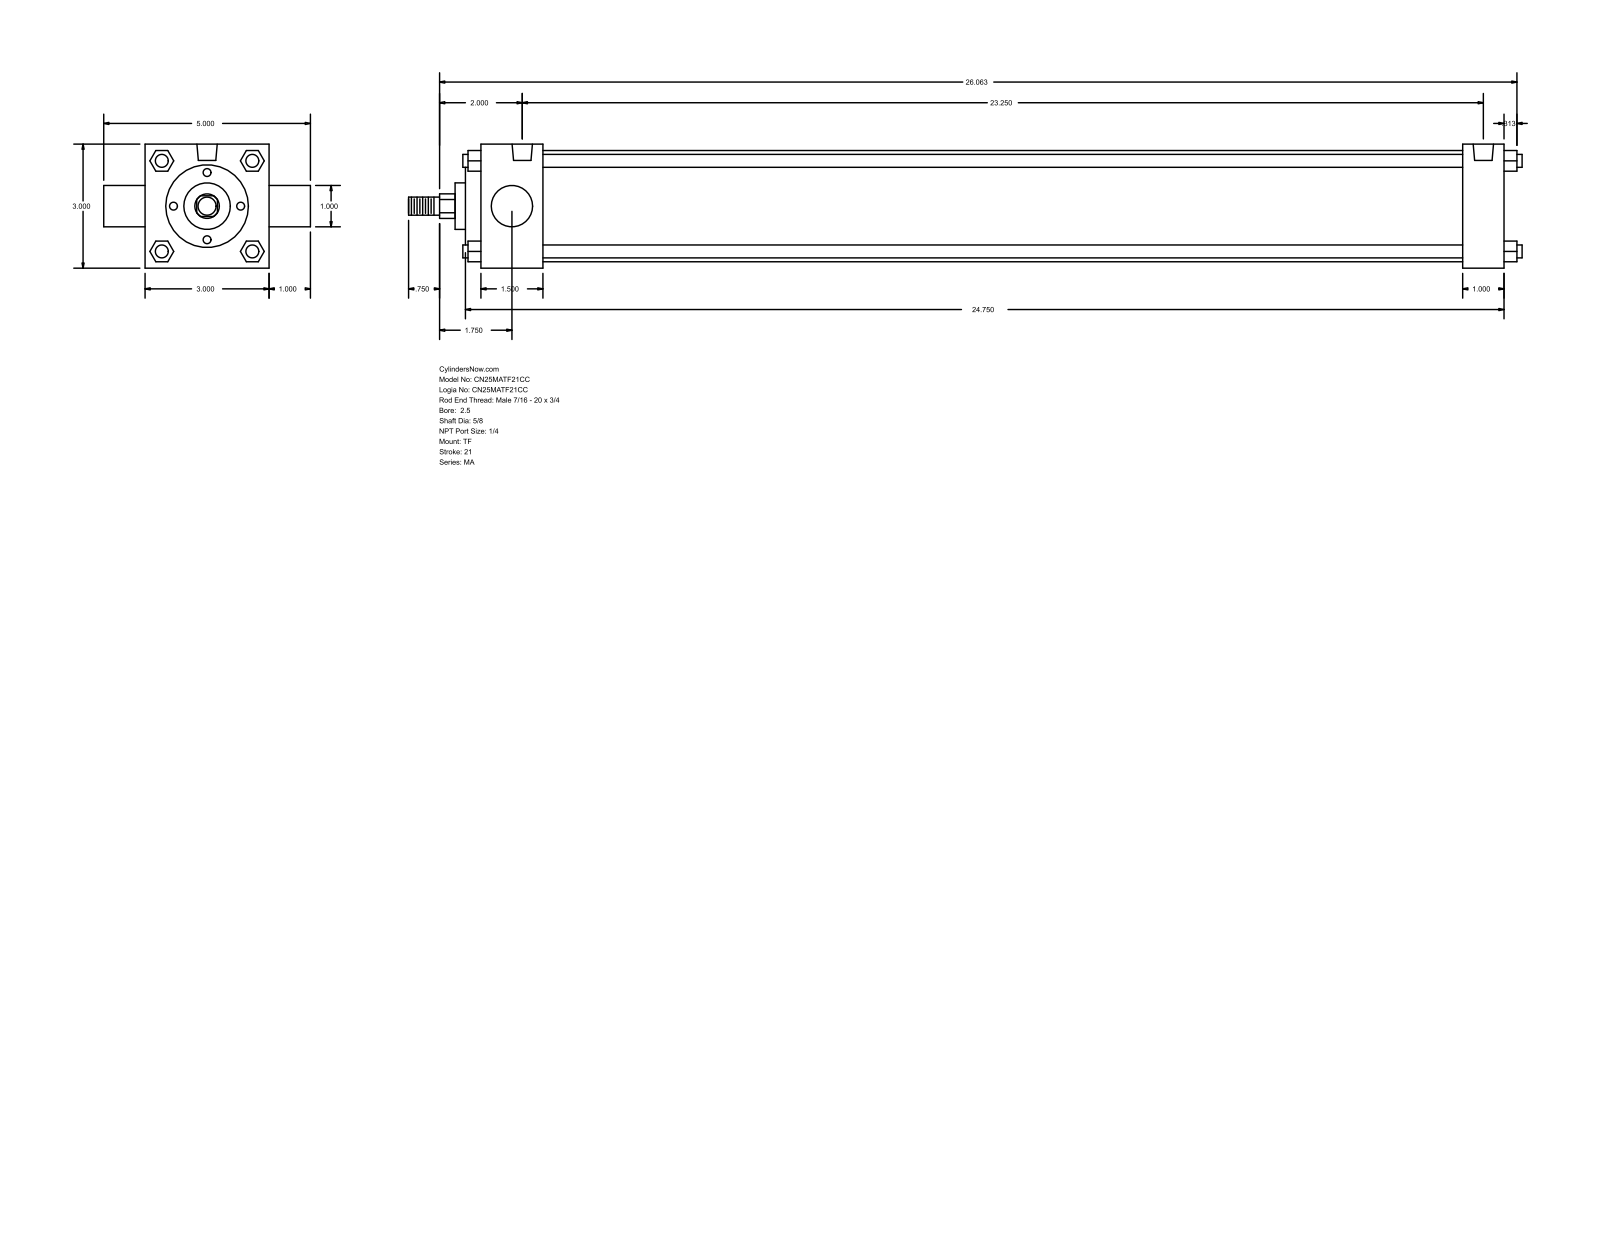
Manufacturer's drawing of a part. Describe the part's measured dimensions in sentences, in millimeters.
The part is named "MA_TF__0250_0.625". Its 3-D file was written by "GSSL Pune (CONFIG_CONTROL_DESIGN)". It is 0 solids with 122 faces: 93 planar, 29 cylindrical and 0 other. Overall it measures 684.21 by 127 by 76.2 millimeters. Round holes: 3 of diameter 7.94, 2 of diameter 12.49. Round bosses or shafts: 4 of diameter 7.94, 1 of diameter 68.33, 1 of diameter 50.8, 1 of diameter 28.57, 1 of diameter 25.4, 1 of diameter 15.88, 1 of diameter 11.11. Partial cylindrical surfaces (rounded edges, fillets, slot ends): 1 of radius 7.54. The main face-to-face distances are 76.2, 628.65, 25.4, 38.1, 603.25, 565.15, 590.55, 12.7, 9.52, 47.62. The hole center spacings are 590.55.
